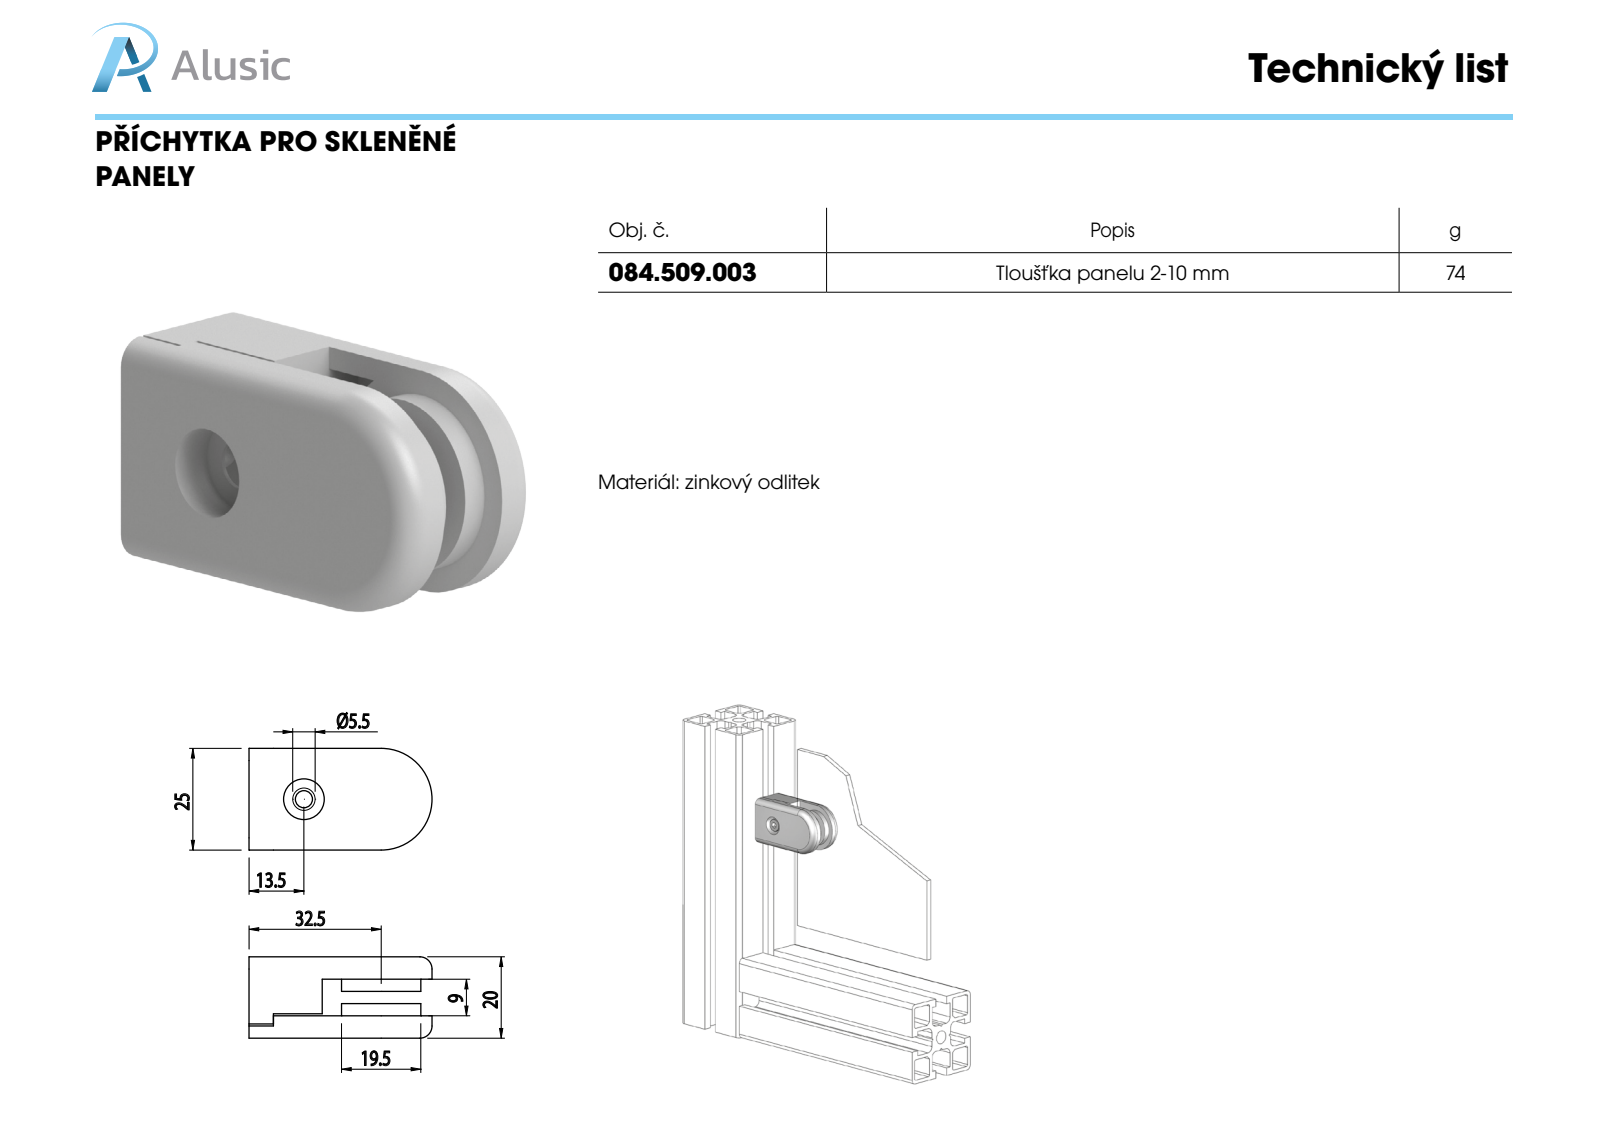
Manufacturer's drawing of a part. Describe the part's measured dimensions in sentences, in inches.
The part is named "084.509.003". Its 3-D file was written by "SolidWorks 2012 (AUTOMOTIVE_DESIGN)". It is 2 solids with 82 faces: 45 planar, 33 cylindrical and 4 other. Overall it measures 1.772 by 0.984 by 0.787 inches. Its volume is 0.775 cubic inches and its surface area 12.59 square inches. Round holes: 2 of diameter 0.157, 2 of diameter 0.217, 1 of diameter 0.165, 1 of diameter 0.394. Round bosses or shafts: 1 of diameter 0.984, 1 of diameter 0.768, 1 of diameter 0.413, 1 of diameter 0.315. Partial cylindrical surfaces (rounded edges, fillets, slot ends): 4 of radius 0.098, 4 of radius 0.118, 1 of radius 0.482. The main face-to-face distances are 0.118, 0.236, 0.098, 0.787, 0.217, 0.335, 0.453, 0.571, 0.354, 0.472. The hole center spacings are 0.295, 0.591.
